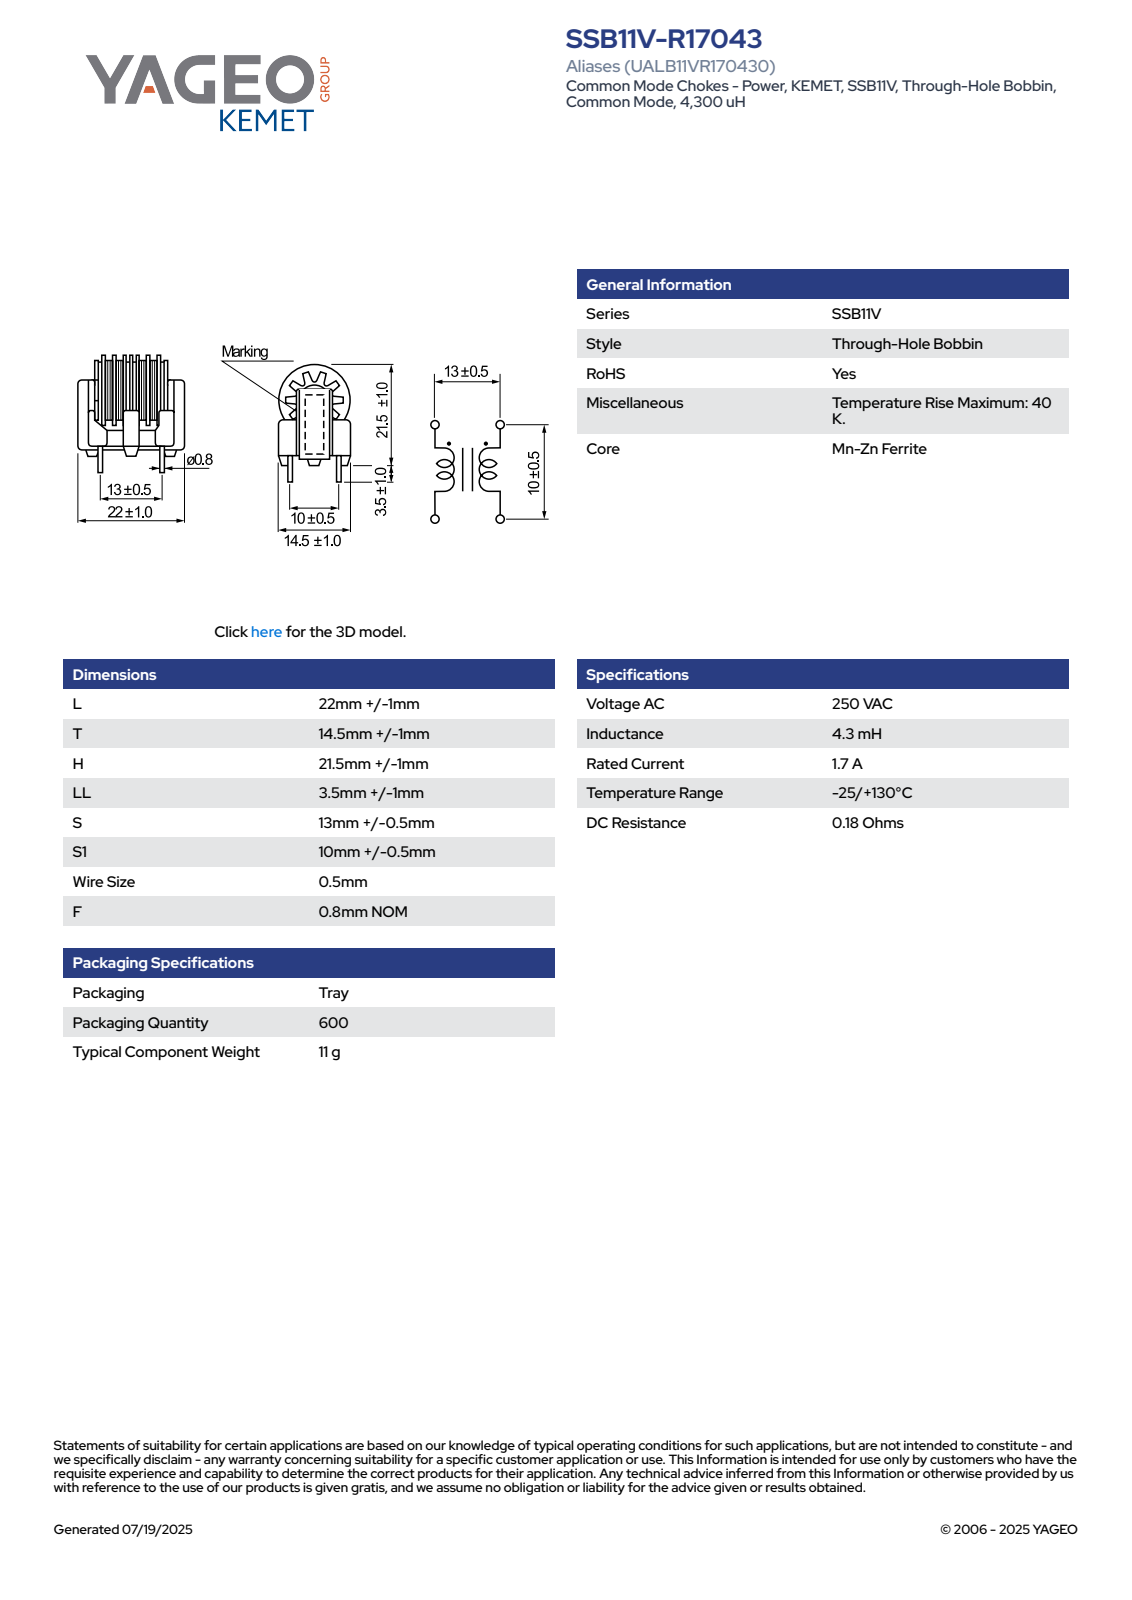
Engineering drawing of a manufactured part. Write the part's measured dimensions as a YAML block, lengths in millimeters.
part_name: "SSB11V(MAX-LOGO)"
step_written_by: "SolidWorks 2018 (AUTOMOTIVE_DESIGN)"
units: millimeters
bodies: {solids: 1, faces: 552, planar: 242, cylindrical: 204, other: 106}
overall_size: [25.95, 23, 15.5]
volume: 4050
surface_area: 5319
round_holes:
  - {diameter: 5.7, count: 1}
  - {diameter: 6, count: 1}
round_bosses_or_shafts:
  - {diameter: 0.8, count: 4}
  - {diameter: 15.1, count: 1}
  - {diameter: 12.6, count: 1}
  - {diameter: 12.5, count: 1}
partial_cylinders:
  - {radius: 0.2, count: 34}
  - {radius: 1.69, count: 20}
  - {radius: 1, count: 16}
  - {radius: 0.5, count: 14}
  - {radius: 0.4, count: 11}
  - {radius: 3.75, count: 1}
  - {radius: 6, count: 1}
  - {radius: 6.5, count: 1}
face_to_face_distances: [4.17, 7.47, 0.6, 4.77, 4.7, 7.48, 4.6, 3.3, 0.8, 5.45]
